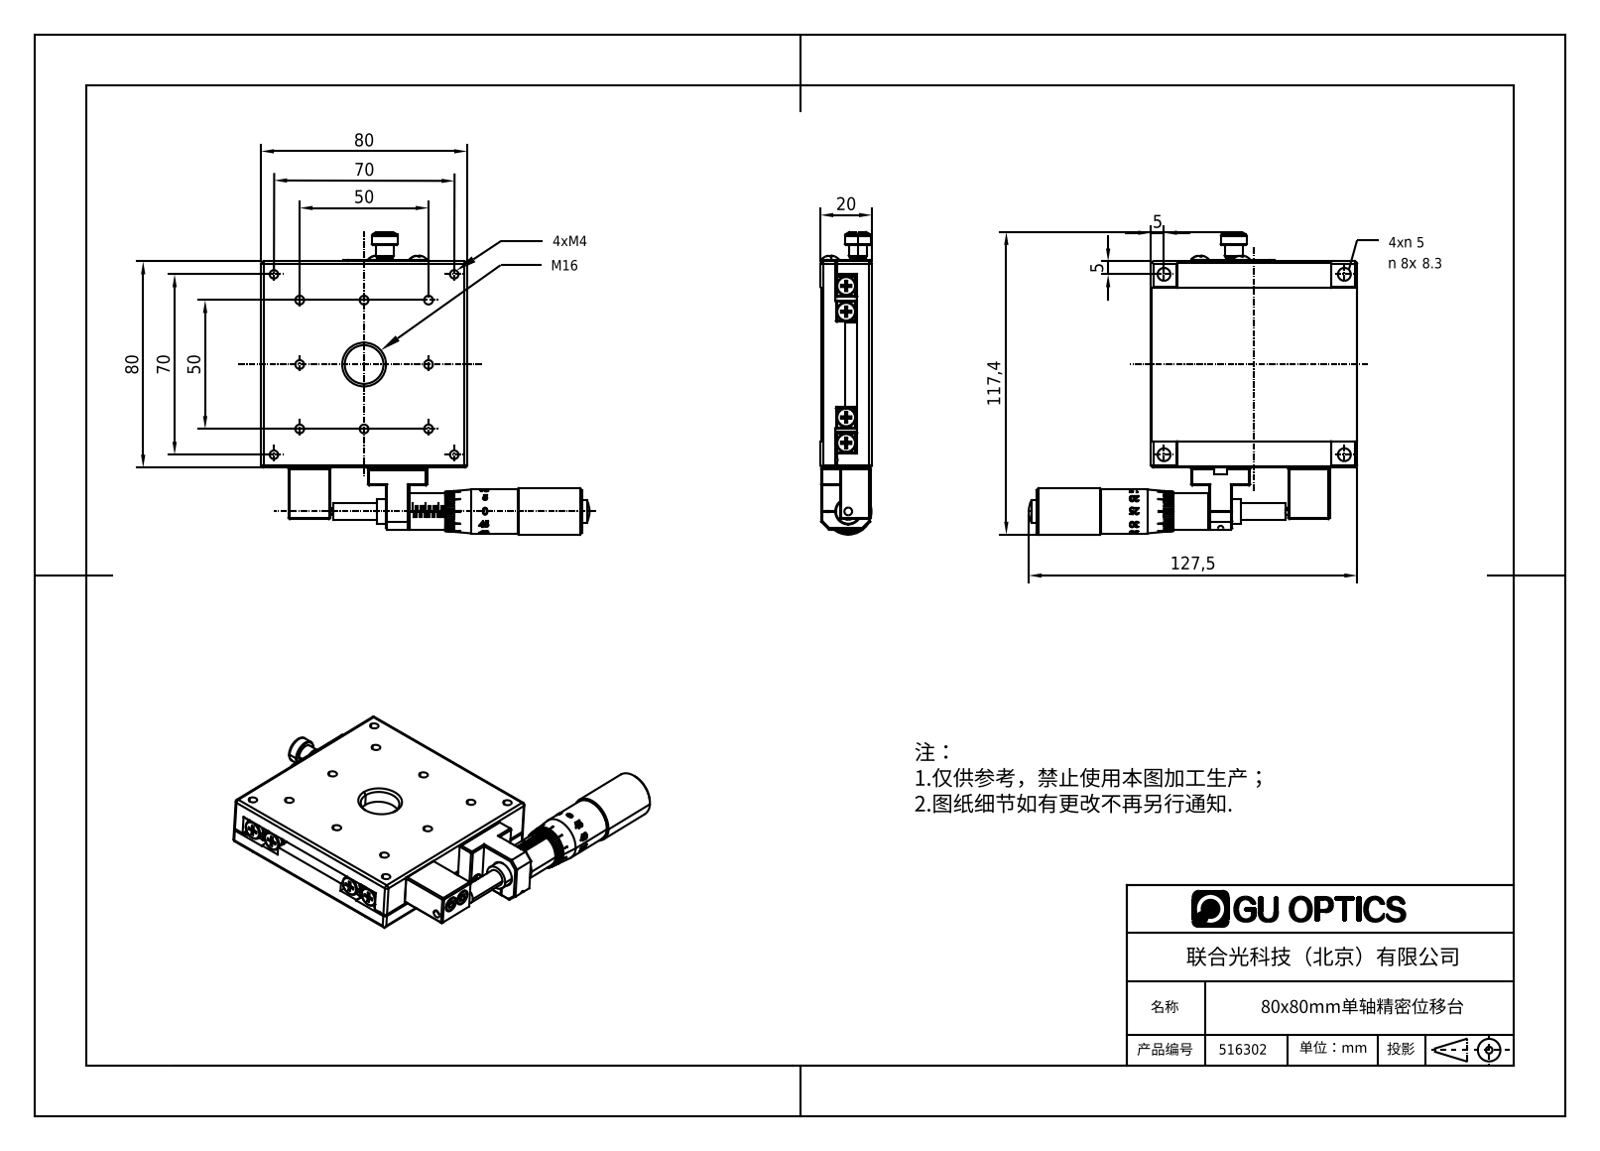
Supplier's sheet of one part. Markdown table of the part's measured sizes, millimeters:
| quantity | value |
| --- | --- |
| part name | 516302 |
| STEP written by | SolidWorks 2020 (CONFIG_CONTROL_DESIGN) |
| units | millimeters |
| bodies | 11 solids, 1655 faces (1048 planar, 256 cylindrical, 351 other) |
| overall size | 127.5 × 117.4 × 20 |
| volume | 132 024 mm³ |
| surface area | 49 108 mm² |
| round holes (diameter × count) | 3.4 × 10, 3.3 × 4, 5 × 4, 6 × 4, 8 × 4, 2.05 × 1, 2.9 × 1, 3 × 1, 9.5 × 1, 14 × 1, 15 × 1 |
| round bosses / shafts (diameter × count) | 3 × 5, 7.5 × 4, 5.5 × 4, 6.9 × 2, 18 × 1, 17 × 1, 10 × 1, 9.2 × 1 |
| partial cylindrical surfaces (radius × count) | 1 × 13, 2 × 4, 1.65 × 2, 2.5 × 1, 6.99 × 1, 8.48 × 1, 8.49 × 1 |
| main face-to-face distances | 14, 5.7, 19.7, 8.3, 4.8, 5.4, 9.2, 10.5, 5.5, 14.3 |
| hole center spacings | 25, 35.36, 36.4, 55.9, 60.83, 69.46, 50, 14.14 |
